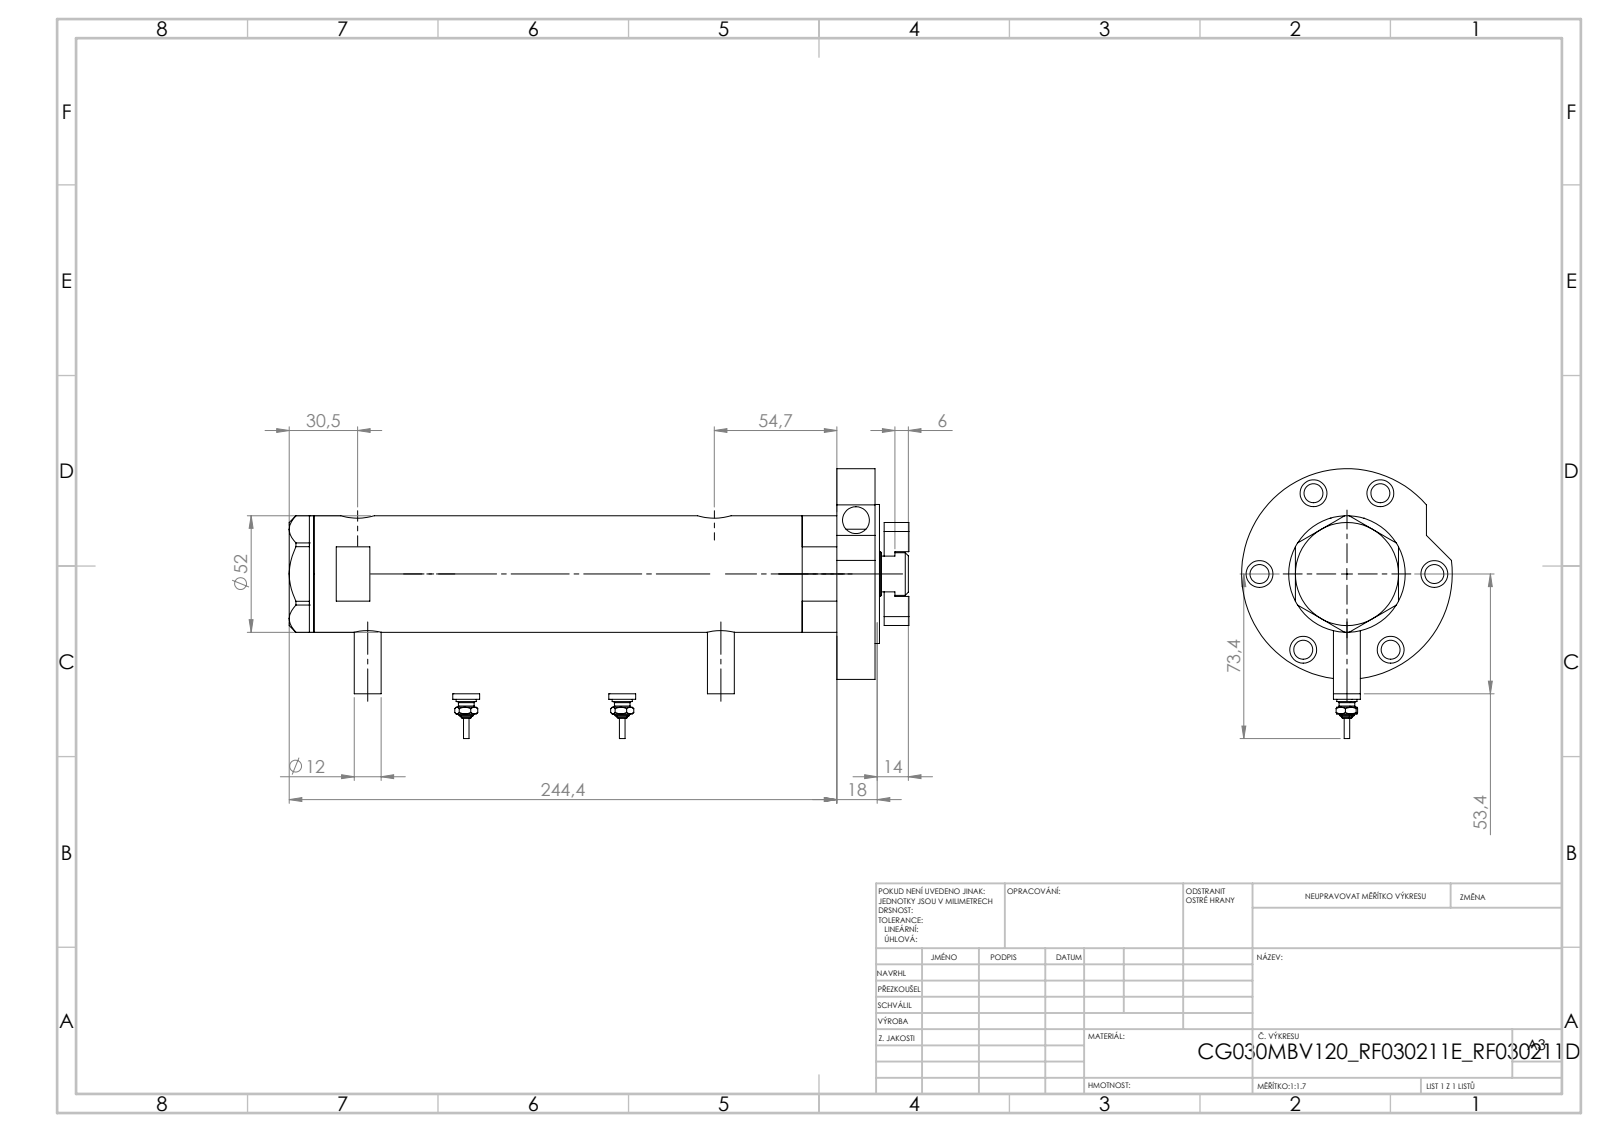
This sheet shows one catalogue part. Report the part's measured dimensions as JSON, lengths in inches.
{"part_name": "V270CG_BACK; V270CG_RF211E; V270CG_MIDDLE; V270CG_FRONT (+3 more)", "step_written_by": "SolidWorks 2019 (CONFIG_CONTROL_DESIGN)", "units": "inches", "bodies": {"solids": 9, "faces": 310, "planar": 128, "cylindrical": 118, "other": 64}, "overall_size": [10.886, 4.74, 3.701], "volume_in3": 35.65, "surface_area_in2": 211, "round_holes": [[0.472, 7], [0.335, 6], [0.201, 4], [0.354, 4], [0.383, 2], [0.492, 2], [0.591, 2], [0.256, 1], [0.787, 1], [0.846, 1], [1.181, 1], [1.299, 1]], "round_bosses_or_shafts": [[0.472, 4], [0.354, 2], [0.276, 2], [0.177, 2], [0.098, 2], [3.701, 1], [2.441, 1], [2.047, 1]], "face_to_face_distances": [0.669, 9.189, 9.858, 0.079, 9.937, 0.433, 7.146, 2.043, 2.713, 2.791], "hole_center_spacings": [1.535, 0.659, 1.479, 1.843, 0.394, 0.881, 0.904, 1.113]}
